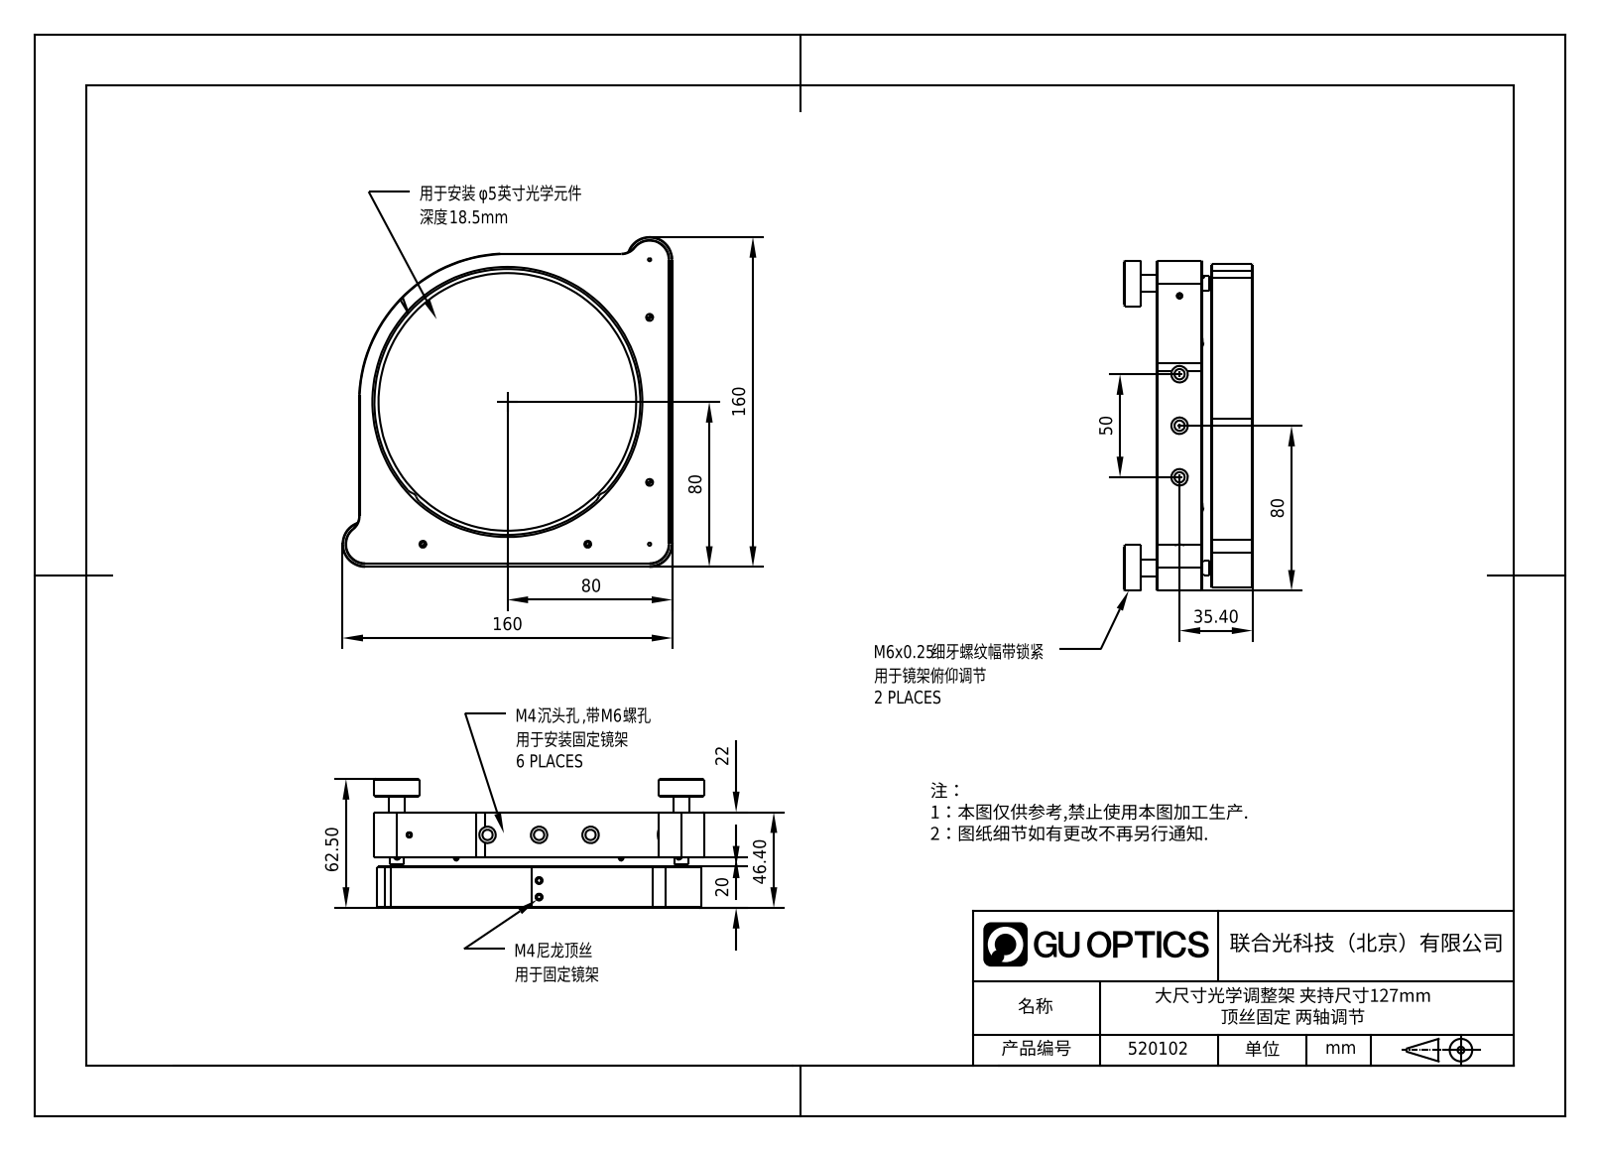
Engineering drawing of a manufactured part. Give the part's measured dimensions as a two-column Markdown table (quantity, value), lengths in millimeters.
| quantity | value |
| --- | --- |
| STEP written by | SolidWorks 2021 (CONFIG_CONTROL_DESIGN) |
| units | millimeters |
| bodies | 0 solids, 341 faces (118 planar, 139 cylindrical, 84 other) |
| overall size | 160 × 160 × 62.5 |
| round holes (diameter × count) | 8 × 10, 3.3 × 6, 5 × 6, 12 × 3, 1.5 × 2, 2.5 × 2, 3 × 2, 6 × 2, 1.2 × 1, 13.5 × 1, 125 × 1, 129 × 1 |
| round bosses / shafts (diameter × count) | 2 × 4, 22 × 2, 8 × 2, 7 × 2, 13 × 1, 12.7 × 1 |
| partial cylindrical surfaces (radius × count) | 1.05 × 8, 5 × 4, 6 × 4, 9.5 × 3, 2.5 × 2, 8 × 2, 10 × 2, 11 × 1 |
| main face-to-face distances | 20, 22, 4.4, 24.4, 26.4, 46.4, 1.5, 150.41, 151.91, 20.5 |
| hole center spacings | 25, 97.58, 28, 30, 33.4, 38, 39.17, 50 |
